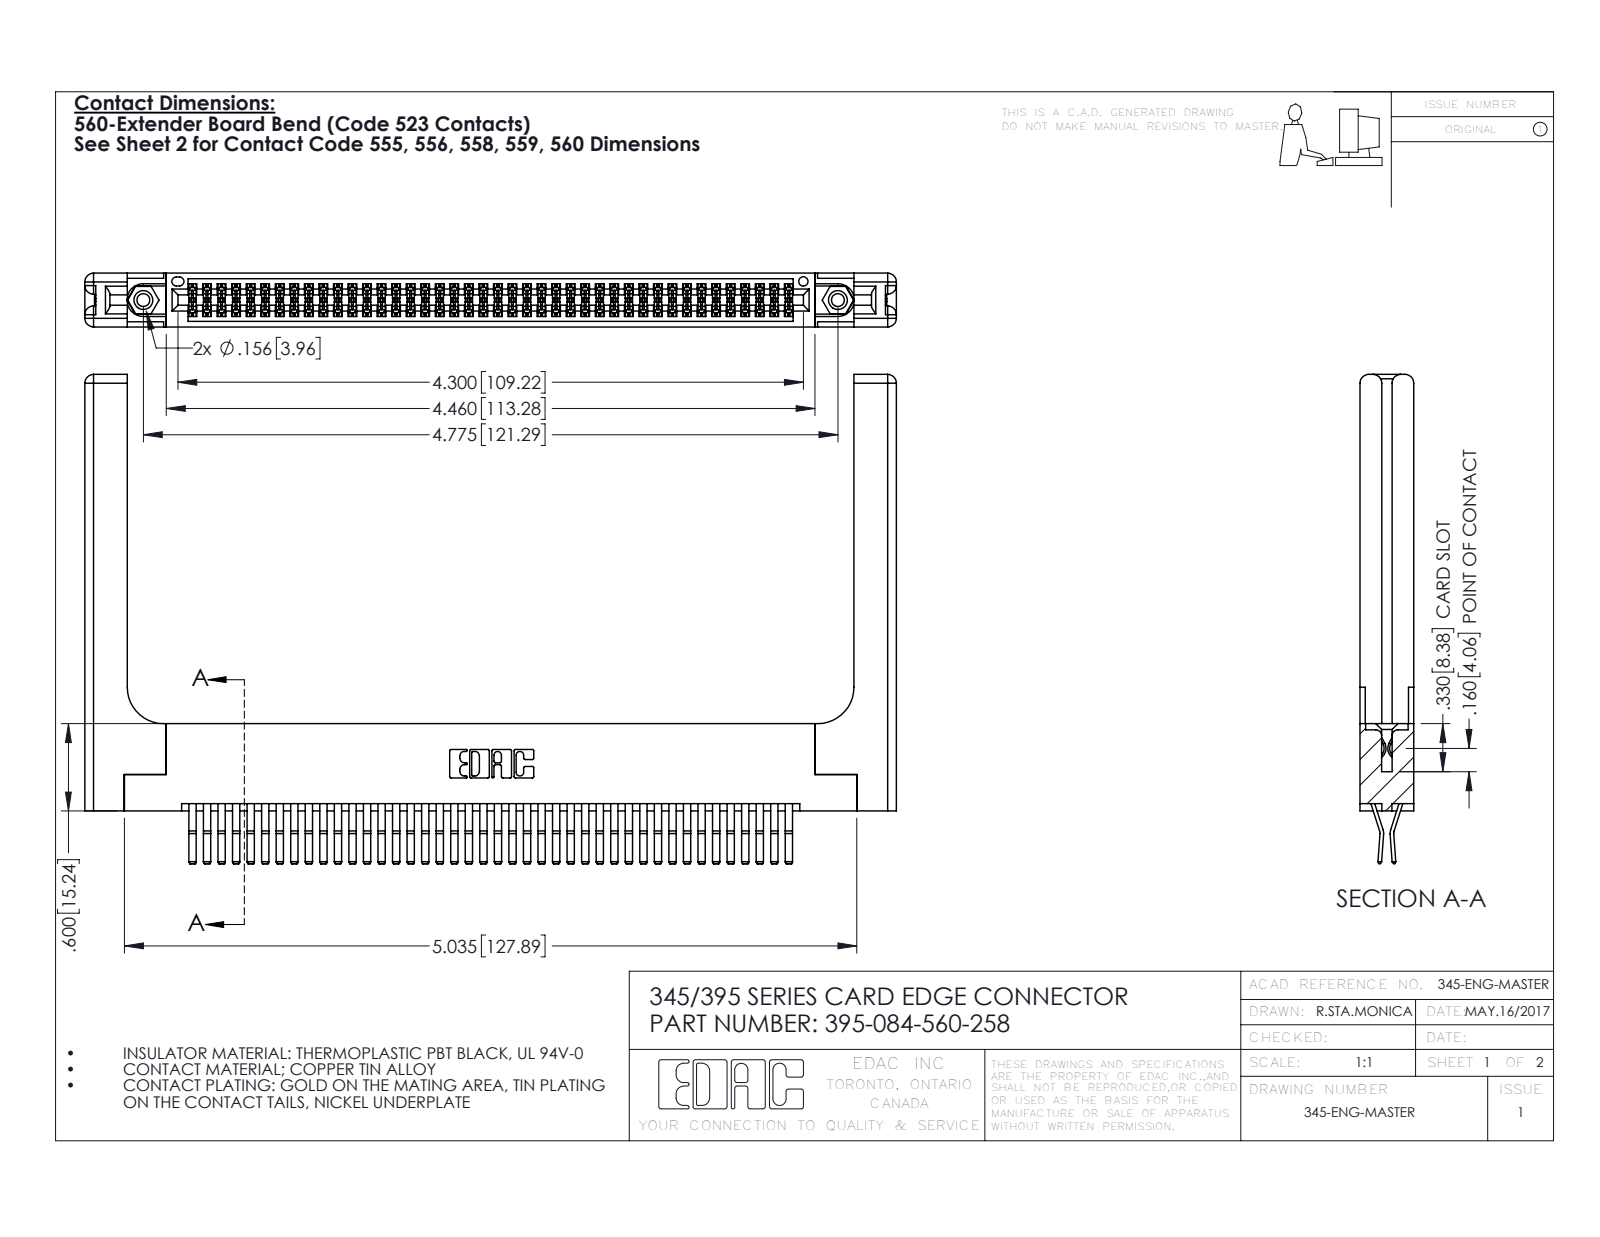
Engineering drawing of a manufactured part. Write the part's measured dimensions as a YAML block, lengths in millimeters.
part_name: "345-250-001_345-250-001-102; 395-084-560-258; 345 Part_Flush Mounting Lugs - 0.156 Dia-TH; 345-220-058_345-220-058 (+1 more)"
step_written_by: "SolidWorks 2016 (CONFIG_CONTROL_DESIGN)"
units: millimeters
bodies: {solids: 89, faces: 4750, planar: 3000, cylindrical: 1690, other: 60}
overall_size: [141.7, 85.4, 9.4]
volume: 22790
surface_area: 27640
round_holes:
  - {diameter: 2.3, count: 2}
  - {diameter: 3.2, count: 2}
  - {diameter: 4, count: 2}
  - {diameter: 1.6, count: 1}
round_bosses_or_shafts:
  - {diameter: 3.9, count: 2}
partial_cylinders:
  - {radius: 0.2, count: 127}
  - {radius: 0.3, count: 22}
  - {radius: 1.5, count: 16}
  - {radius: 0.2, count: 6}
  - {radius: 0.8, count: 6}
  - {radius: 0.7, count: 3}
  - {radius: 0.3, count: 2}
  - {radius: 0.4, count: 2}
face_to_face_distances: [1.8, 9.4, 7.6, 0.6, 5.1, 2.5, 6.9, 5.7, 3.8, 3.8]
hole_center_spacings: [6.9, 115.3, 121.3]
